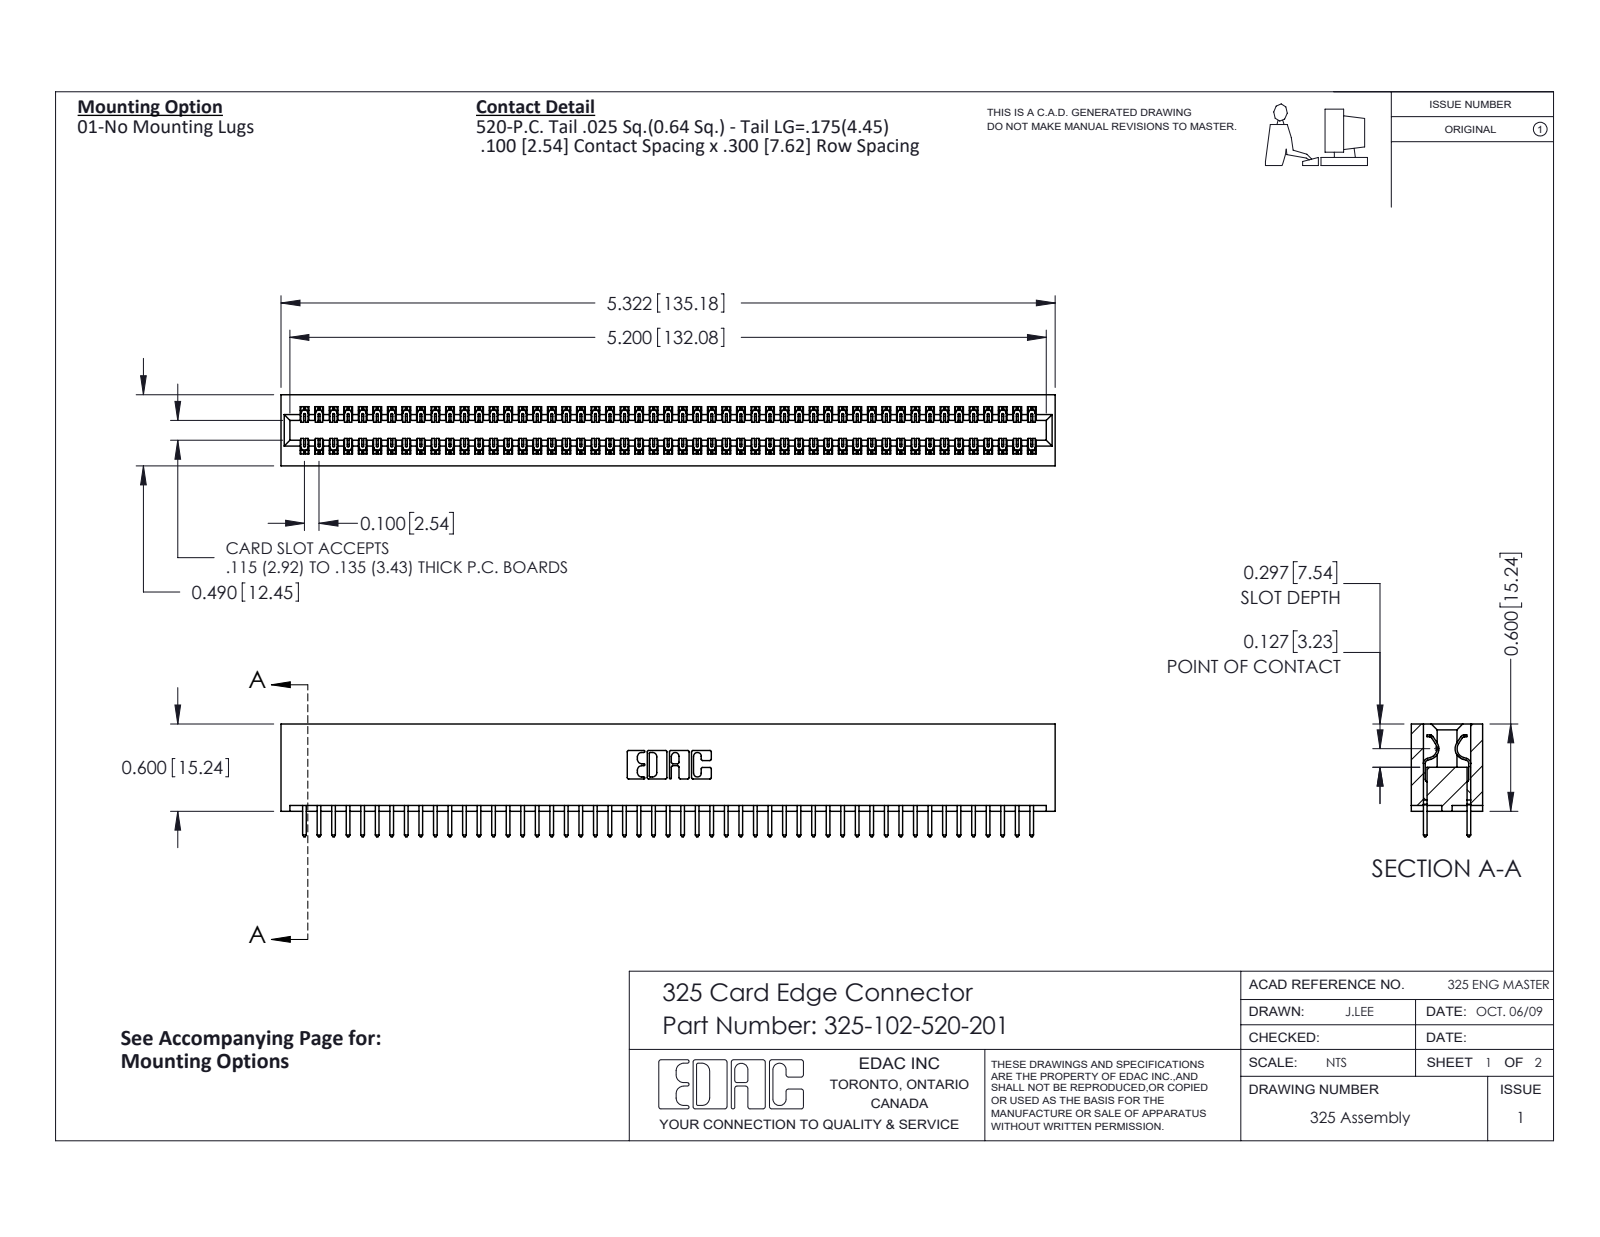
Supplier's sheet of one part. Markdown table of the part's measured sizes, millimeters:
| quantity | value |
| --- | --- |
| part name | 325-292-001_325-293-120; 325-102-520-201; 325 Part_Lugless |
| STEP written by | SolidWorks 2016 (CONFIG_CONTROL_DESIGN) |
| units | millimeters |
| bodies | 103 solids, 5410 faces (3738 planar, 1672 cylindrical, 0 other) |
| overall size | 135.2 × 19.7 × 12.4 |
| volume | 18 120 mm³ |
| surface area | 22 610 mm² |
| partial cylindrical surfaces (radius × count) | 0.2 × 153, 0.3 × 102, 0.3 × 22, 0.2 × 6, 0.8 × 6, 0.7 × 3, 0.4 × 2, 0.6 × 2 |
| main face-to-face distances | 2.1, 10.3, 7.6, 12.4, 2.7, 9.7, 0.6, 8.3, 7, 14.2 |
